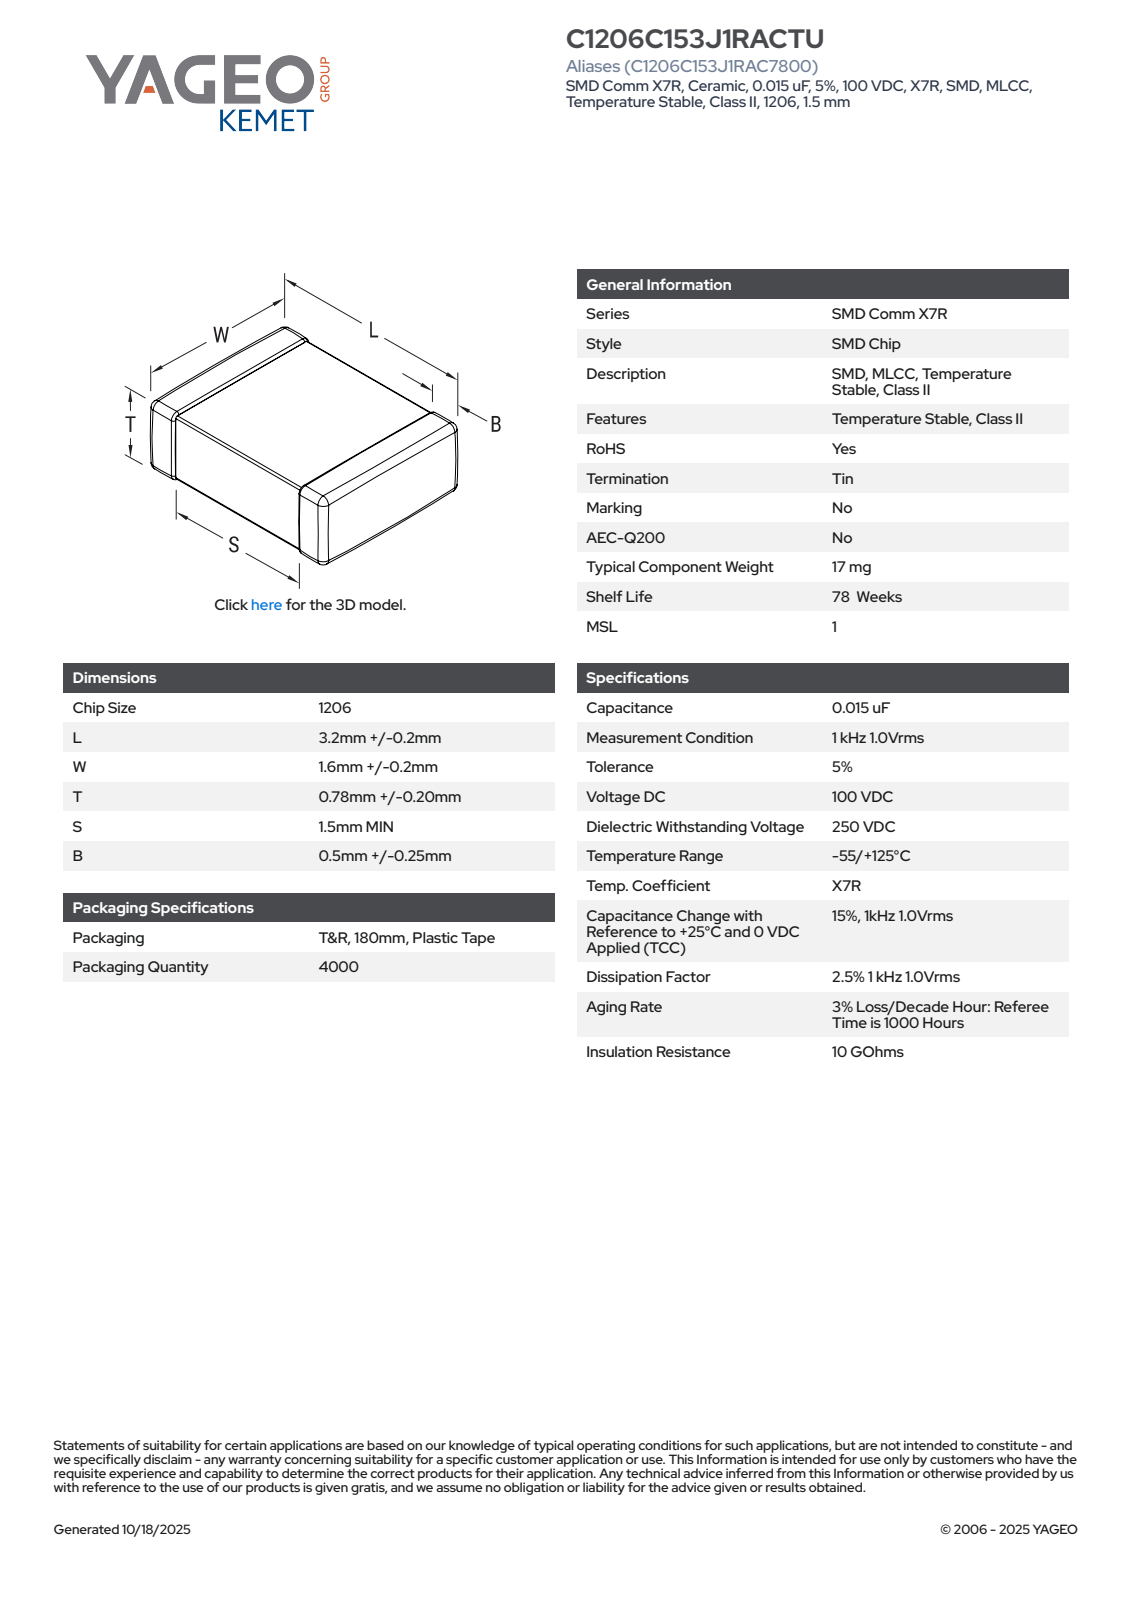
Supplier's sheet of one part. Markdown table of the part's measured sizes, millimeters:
| quantity | value |
| --- | --- |
| part name | CCS_CCSTDNOS_1206_L3.4W1.8T0.98B0.75 |
| STEP written by | SolidWorks 2021 (AUTOMOTIVE_DESIGN) |
| units | millimeters |
| bodies | 4 solids, 125 faces (71 planar, 38 cylindrical, 16 other) |
| overall size | 3.4 × 1.8 × 0.98 |
| volume | 6 mm³ |
| surface area | 22 mm² |
| main face-to-face distances | 0.94, 0.9, 1.76, 0.98, 1.72, 3.4, 1.8, 0.95, 0.91, 0.99 |
